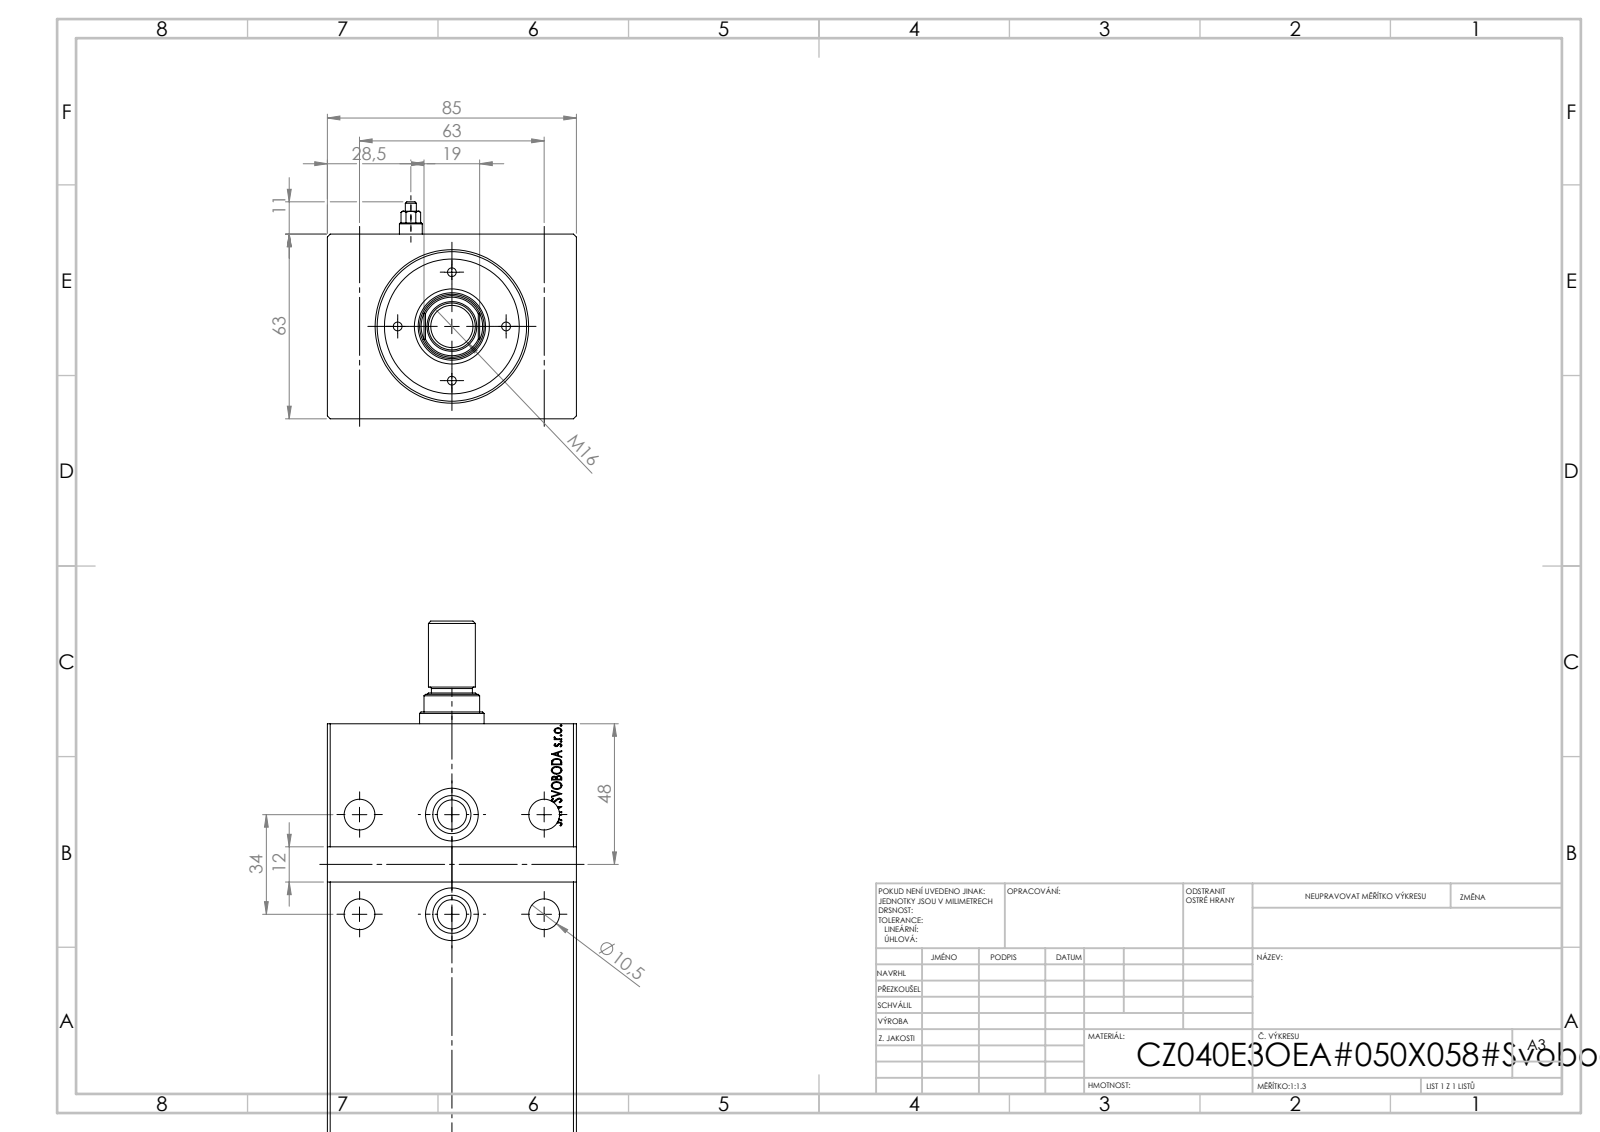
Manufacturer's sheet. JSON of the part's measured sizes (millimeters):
{"step_written_by": "SolidWorks 2019 (CONFIG_CONTROL_DESIGN)", "units": "millimeters", "bodies": {"solids": 1, "faces": 797, "planar": 383, "cylindrical": 30, "other": 384}, "overall_size": [151, 85, 63], "volume_mm3": 604657, "surface_area_mm2": 81063, "round_holes": [[10.5, 4], [8, 2], [10, 2], [18, 2], [36, 1], [40, 1], [51, 1]], "round_bosses_or_shafts": [[13, 2]], "face_to_face_distances": [63, 85, 151, 135.7, 15.3, 2, 61, 150.8, 15.1, 10], "hole_center_spacings": [31.5, 46.35, 34, 63, 71.59, 14.56, 17.95, 33.11]}
